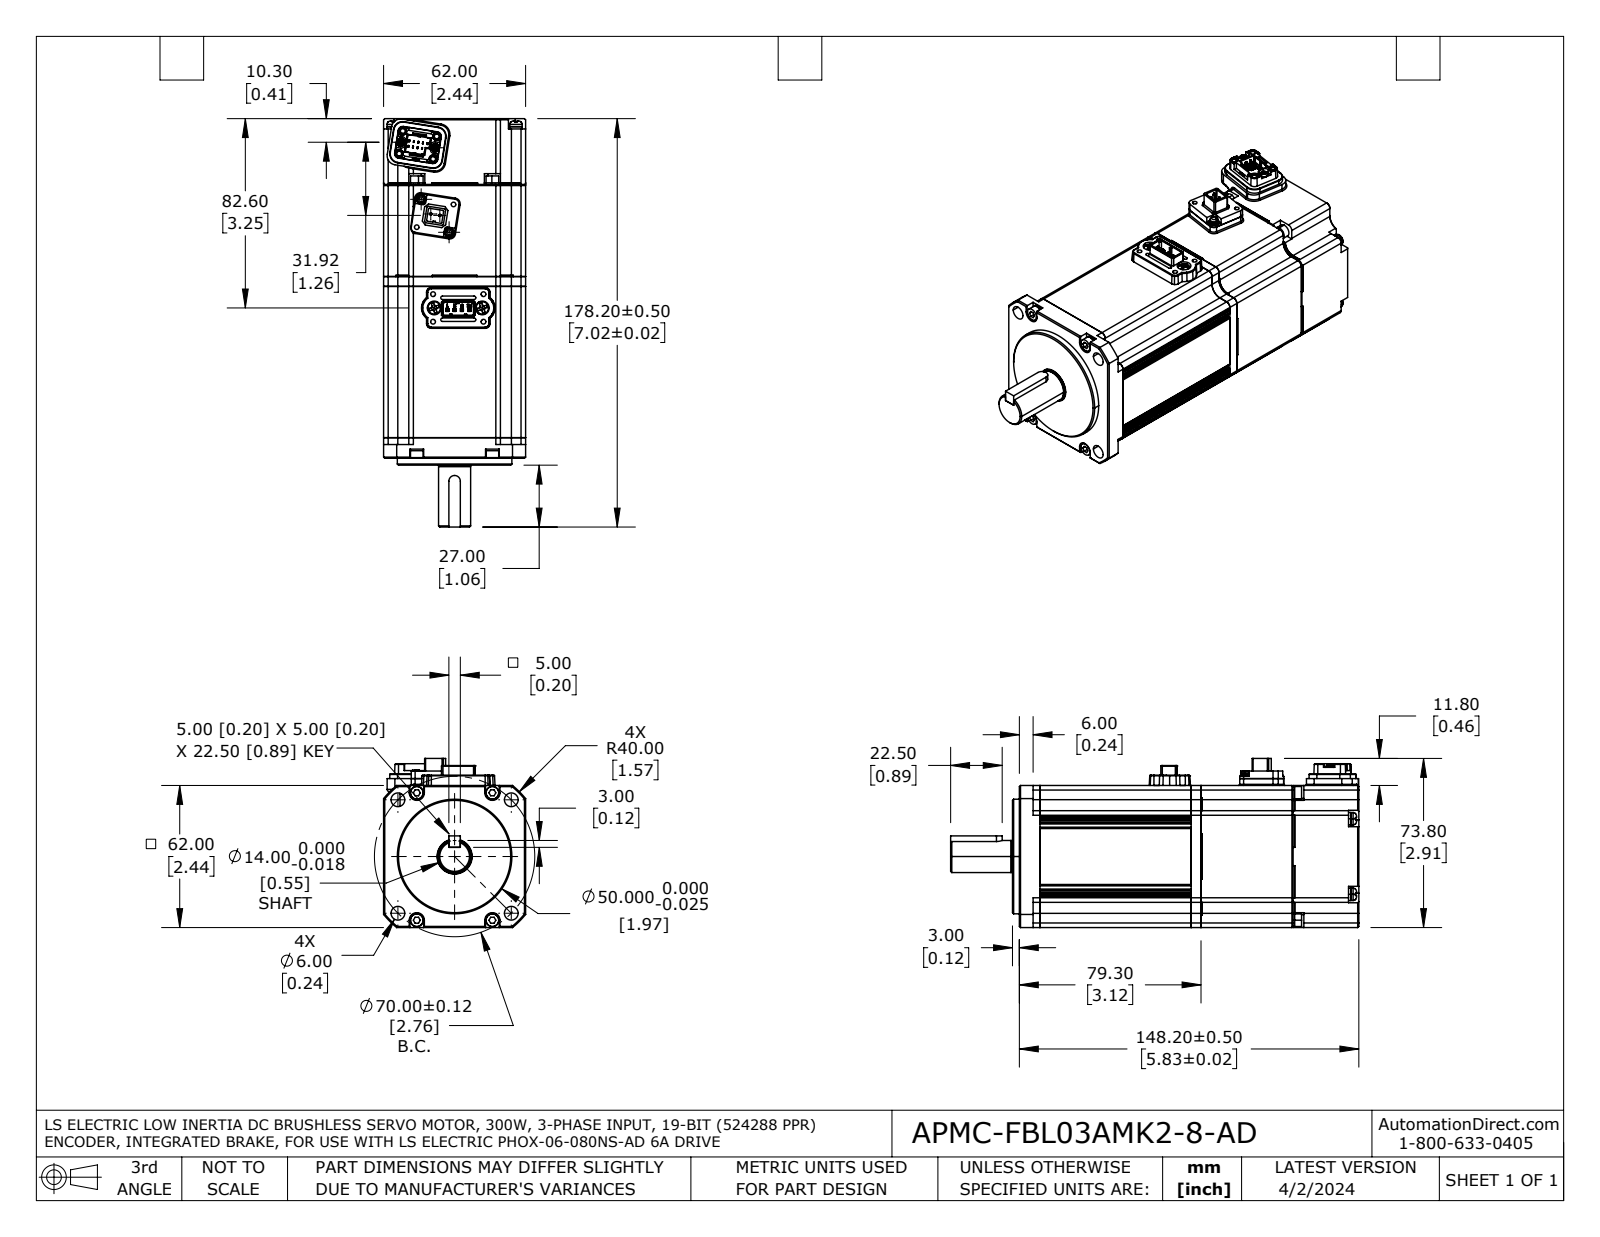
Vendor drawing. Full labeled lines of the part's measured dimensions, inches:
Part name (STEP PRODUCT): APMC-FBL03AMK2-8-AD
STEP written by: SolidWorks 2021 (AUTOMOTIVE_DESIGN)
Units: inches
Bodies: 51 solids, 2195 faces (1289 planar, 673 cylindrical, 233 other)
Overall size (bounding box): 7.016 × 2.906 × 2.441
Volume: 31.5 in³ · Surface area: 160.5 in²
Round holes (diameter × count): ⌀0.083 ×10, ⌀0.138 ×8, ⌀0.118 ×6, ⌀0.236 ×6, ⌀0.079 ×4, ⌀0.122 ×4, ⌀0.039 ×2, ⌀0.13 ×1, ⌀0.134 ×1, ⌀0.512 ×1, ⌀0.602 ×1
Round bosses / shafts (diameter × count): ⌀0.213 ×6, ⌀0.22 ×4, ⌀0.217 ×4, ⌀0.118 ×4, ⌀0.165 ×2, ⌀0.142 ×2, ⌀0.138 ×2, ⌀0.087 ×2
Partial cylindrical surfaces — rounded edges, fillets, slot ends (radius × count): R0.008 ×20, R0.012 ×20, R0.039 ×14, R0.079 ×12, R0.006 ×9, R0.118 ×8, R0.018 ×7, R0.004 ×6
Main face-to-face distances: 2.441, 0.169, 0.028, 0.02, 2.598, 2.768, 1.752, 1.583, 4.35, 1.61
Hole centre spacings: 0.237, 0.335, 0.346, 0.602, 0.63, 0.879, 1.239, 1.273
